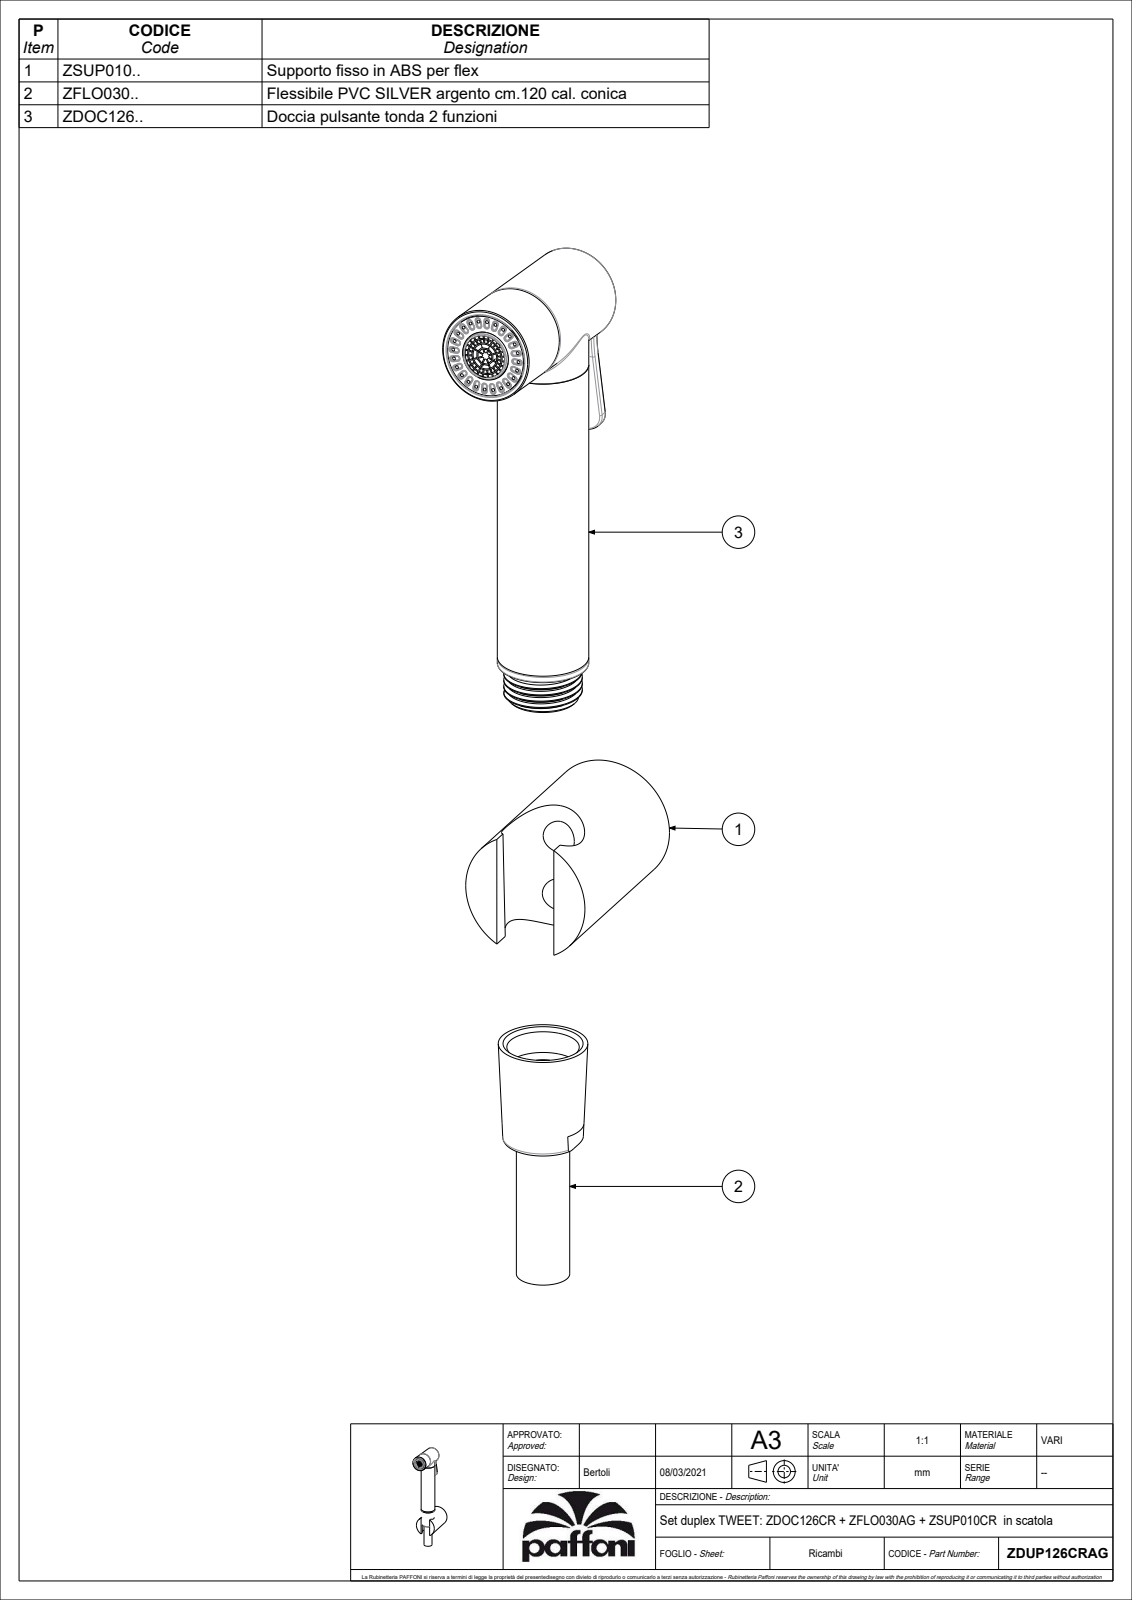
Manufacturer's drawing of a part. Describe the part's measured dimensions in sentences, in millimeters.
The part is named "ZDUP126CRAG". Its 3-D file was written by "CREO PARAMETRIC BY PTC INC, 2022124 (CONFIG_CONTROL_DESIGN)". It is 0 solids with 657 faces: 237 planar, 153 cylindrical and 267 other. Overall it measures 183.35 by 78.34 by 34.5 millimeters. Round holes: 2 of diameter 9, 1 of diameter 29.5. Round bosses or shafts: 2 of diameter 11, 1 of diameter 34.5, 1 of diameter 25, 1 of diameter 24, 1 of diameter 21.9. Partial cylindrical surfaces (rounded edges, fillets, slot ends): 58 of radius 0.1, 43 of radius 0.2, 6 of radius 0.5, 4 of radius 0.3, 4 of radius 2.5, 2 of radius 30, 1 of radius 6.7, 1 of radius 8.44. The main face-to-face distances are 0.46, 19.06, 18.6, 52.5, 2.99, 6.8, 34.99, 35.45, 54.05, 5.25. The hole center spacings are 8.25, 16.5.
